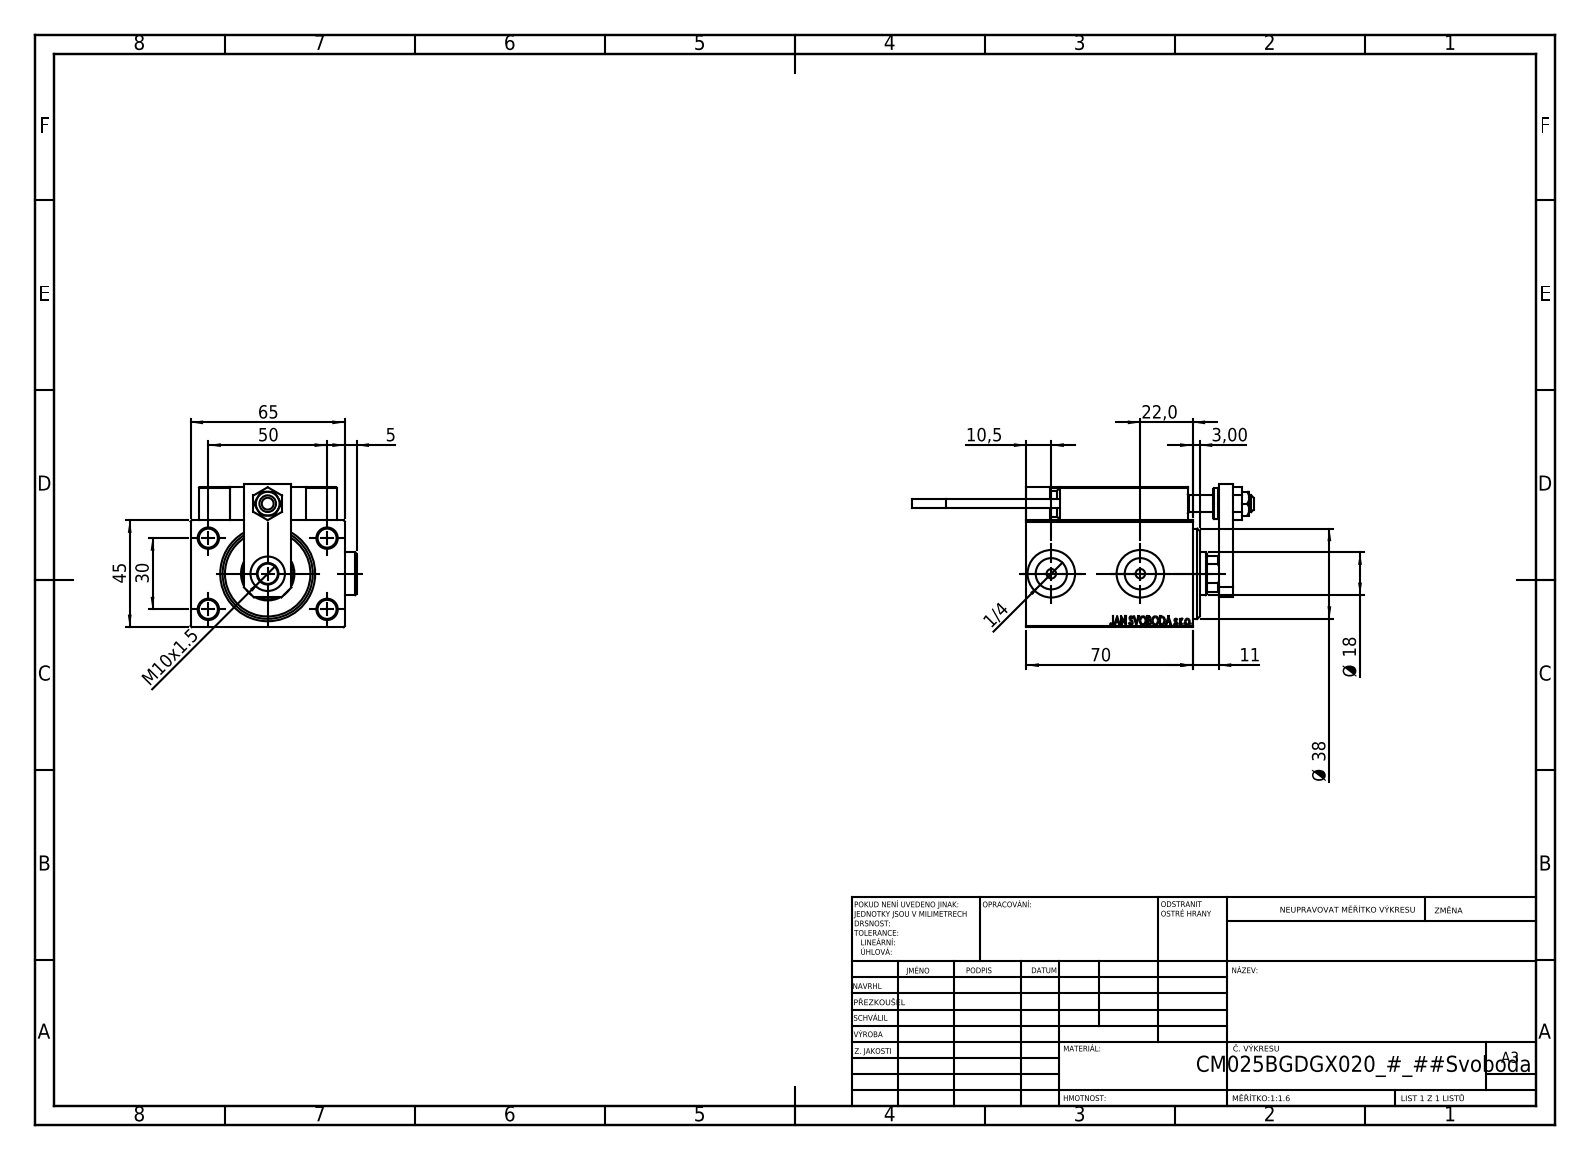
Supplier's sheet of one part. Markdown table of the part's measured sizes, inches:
| quantity | value |
| --- | --- |
| part name | NUT_D12; SWITCH X; TYC_L79; SWITCH_X_FRONT_BACK (+7 more) |
| STEP written by | SolidWorks 2019 (CONFIG_CONTROL_DESIGN) |
| units | inches |
| bodies | 26 solids, 1372 faces (595 planar, 200 cylindrical, 577 other) |
| overall size | 5.657 × 2.752 × 2.382 |
| volume | 14.49 in³ |
| surface area | 104.2 in² |
| round holes (diameter × count) | 0.315 × 9, 0.157 × 6, 0.126 × 4, 0.197 × 2, 0.518 × 2, 0.787 × 2, 0.276 × 1, 0.335 × 1, 0.571 × 1, 0.709 × 1, 0.846 × 1, 0.886 × 1 |
| round bosses / shafts (diameter × count) | 0.709 × 2, 0.197 × 2, 0.15 × 2, 0.512 × 1, 0.433 × 1 |
| partial cylindrical surfaces (radius × count) | 0.012 × 30, 0.118 × 2, 0.335 × 1 |
| main face-to-face distances | 1.772, 2.323, 0.551, 2.559, 0.236, 0.197, 0.748, 0.512, 0.138, 2.283 |
| hole center spacings | 1.148, 0.448, 0.787, 0.87, 1.138, 1.165, 1.169, 1.181 |
